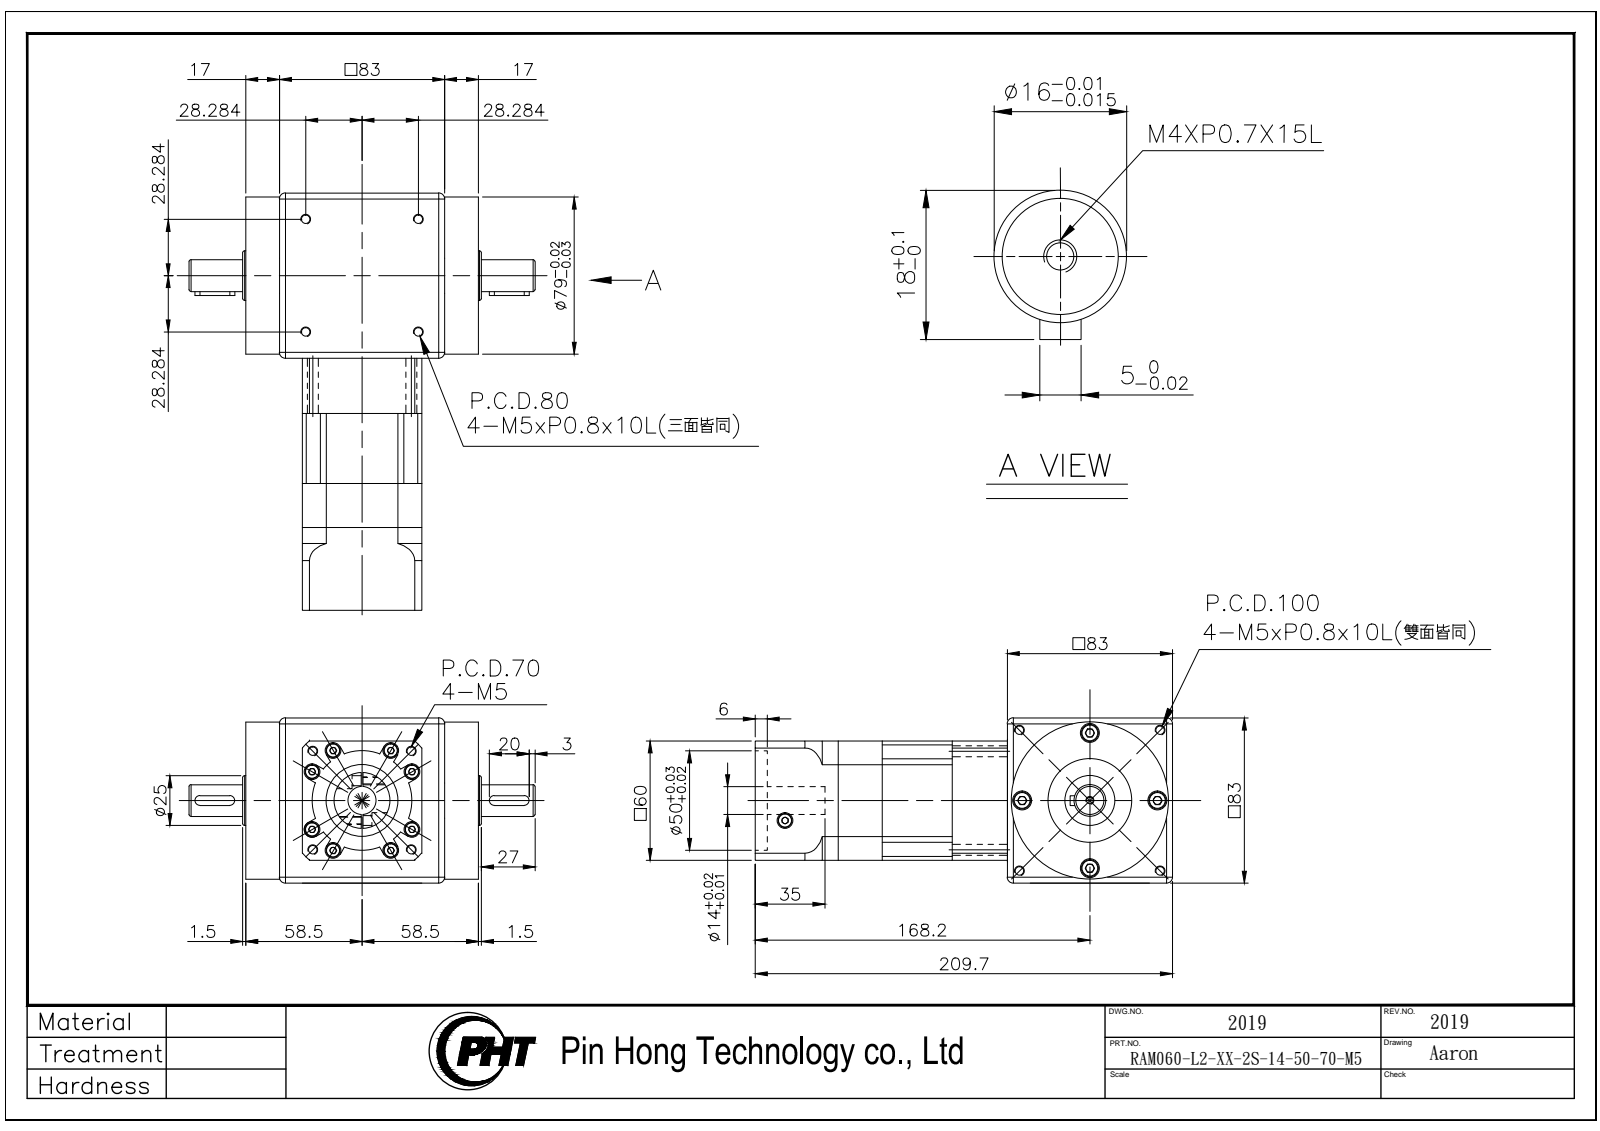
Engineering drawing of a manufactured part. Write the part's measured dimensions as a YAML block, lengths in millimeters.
part_name: "RAM060-L2-XX-2S-14-50-70-M5_2019"
step_written_by: "SolidWorks 2016 (AUTOMOTIVE_DESIGN)"
units: millimeters
bodies: {solids: 6, faces: 713, planar: 330, cylindrical: 247, other: 136}
overall_size: [209.7, 174, 83]
volume: 1134000
surface_area: 136564
round_holes:
  - {diameter: 4.2, count: 16}
  - {diameter: 8, count: 10}
  - {diameter: 4.5, count: 8}
  - {diameter: 5.5, count: 8}
  - {diameter: 9.5, count: 4}
  - {diameter: 3.3, count: 1}
  - {diameter: 4, count: 1}
  - {diameter: 14, count: 1}
  - {diameter: 36, count: 1}
round_bosses_or_shafts:
  - {diameter: 8.5, count: 8}
  - {diameter: 7, count: 8}
  - {diameter: 79, count: 1}
  - {diameter: 55, count: 1}
  - {diameter: 42, count: 1}
  - {diameter: 28, count: 1}
  - {diameter: 25, count: 1}
  - {diameter: 16, count: 1}
partial_cylinders:
  - {radius: 2.5, count: 4}
  - {radius: 5, count: 4}
  - {radius: 25, count: 1}
  - {radius: 35, count: 1}
  - {radius: 40, count: 1}
  - {radius: 57.15, count: 1}
face_to_face_distances: [71.5, 11.5, 83, 60, 27.7, 57.35, 85.05, 22.15, 35.2, 62.9]
hole_center_spacings: [29, 10.26, 14.14, 39.25, 41.01, 42.9, 50.9, 53.15]
